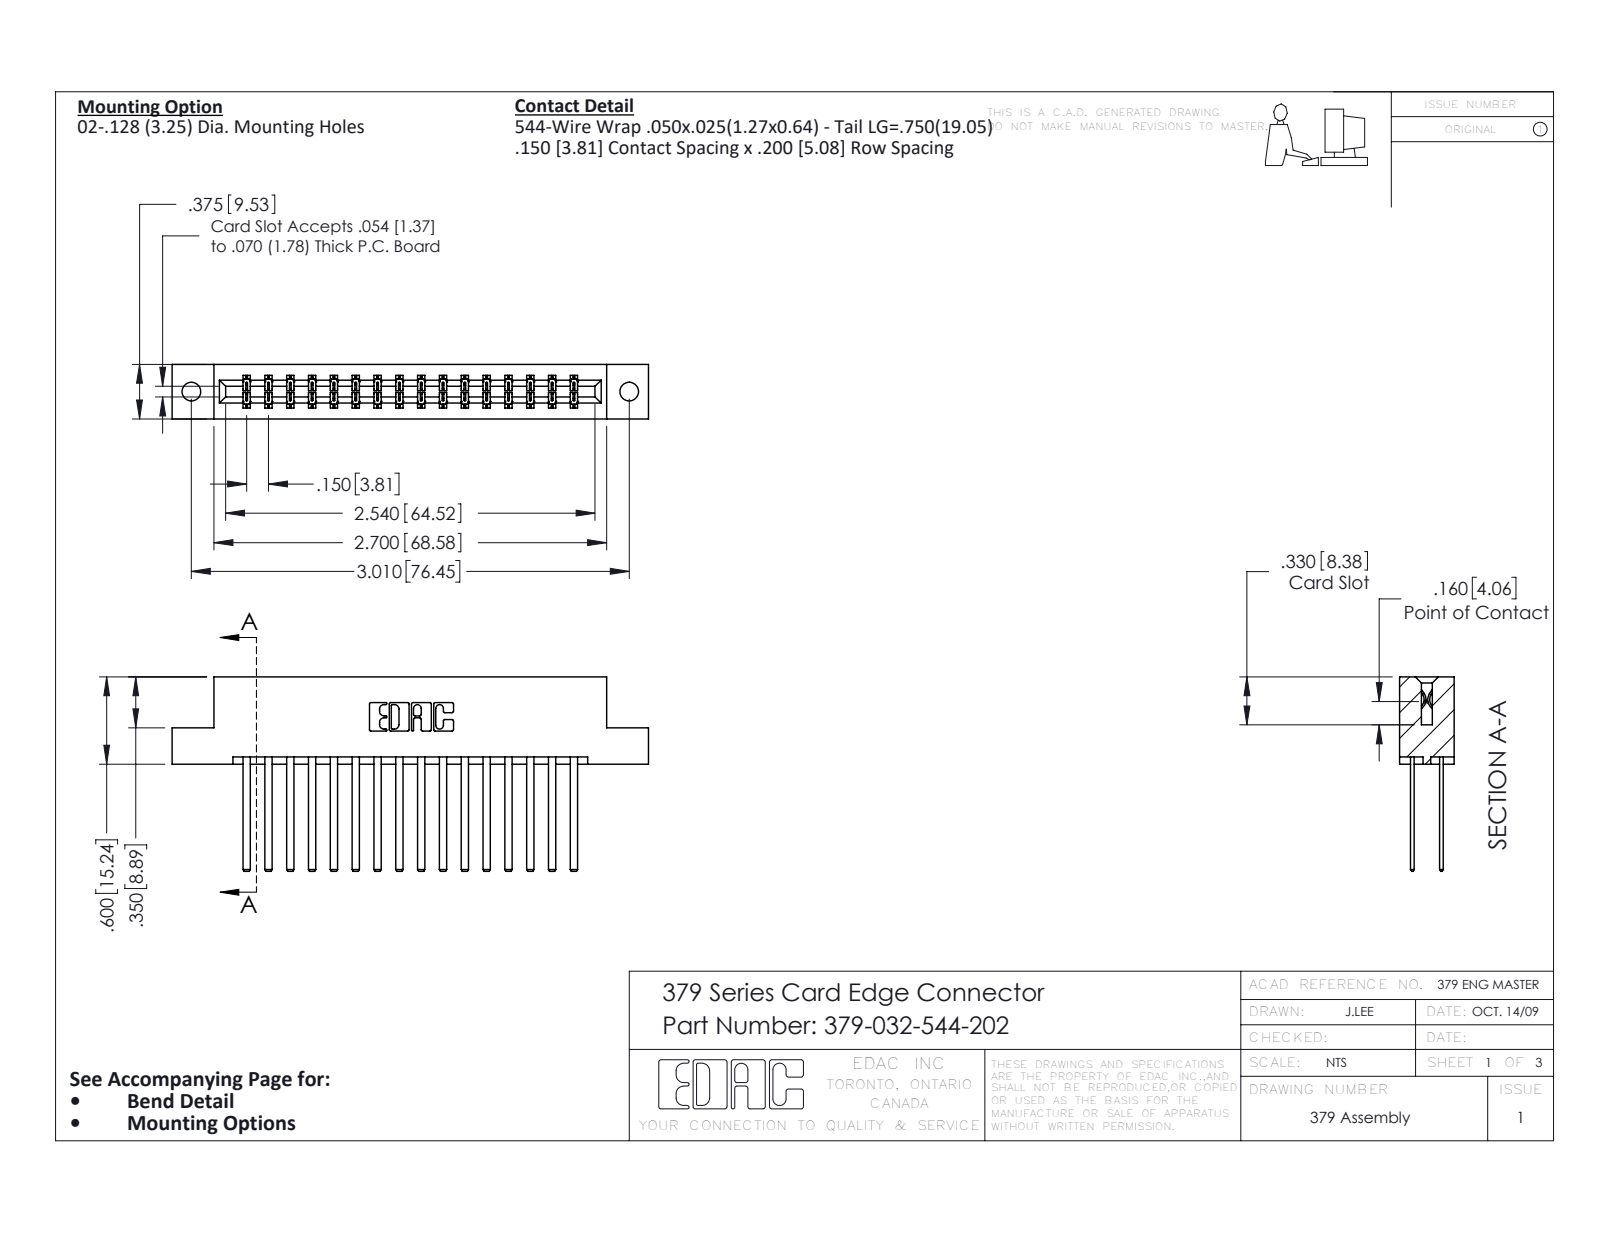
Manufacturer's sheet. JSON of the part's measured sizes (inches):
{"part_name": "379 Part_Flush - .128 Dia; 345-292-001_345-293-144; 379-032-544-202", "step_written_by": "SolidWorks 2020 (CONFIG_CONTROL_DESIGN)", "units": "inches", "bodies": {"solids": 33, "faces": 1586, "planar": 1094, "cylindrical": 492, "other": 0}, "overall_size": [3.275, 1.337, 0.375], "volume_in3": 0.546, "surface_area_in2": 17.06, "round_holes": [[0.128, 2]], "partial_cylinders_radius": [[0.006, 48], [0.01, 22], [0.007, 6], [0.031, 6], [0.026, 3], [0.014, 2], [0.022, 2], [0.024, 2]], "face_to_face_distances": [0.3, 0.2, 0.075, 0.1, 0.275, 0.15, 0.025, 0.225, 0.6, 0.375], "hole_center_spacings": [3.01]}
